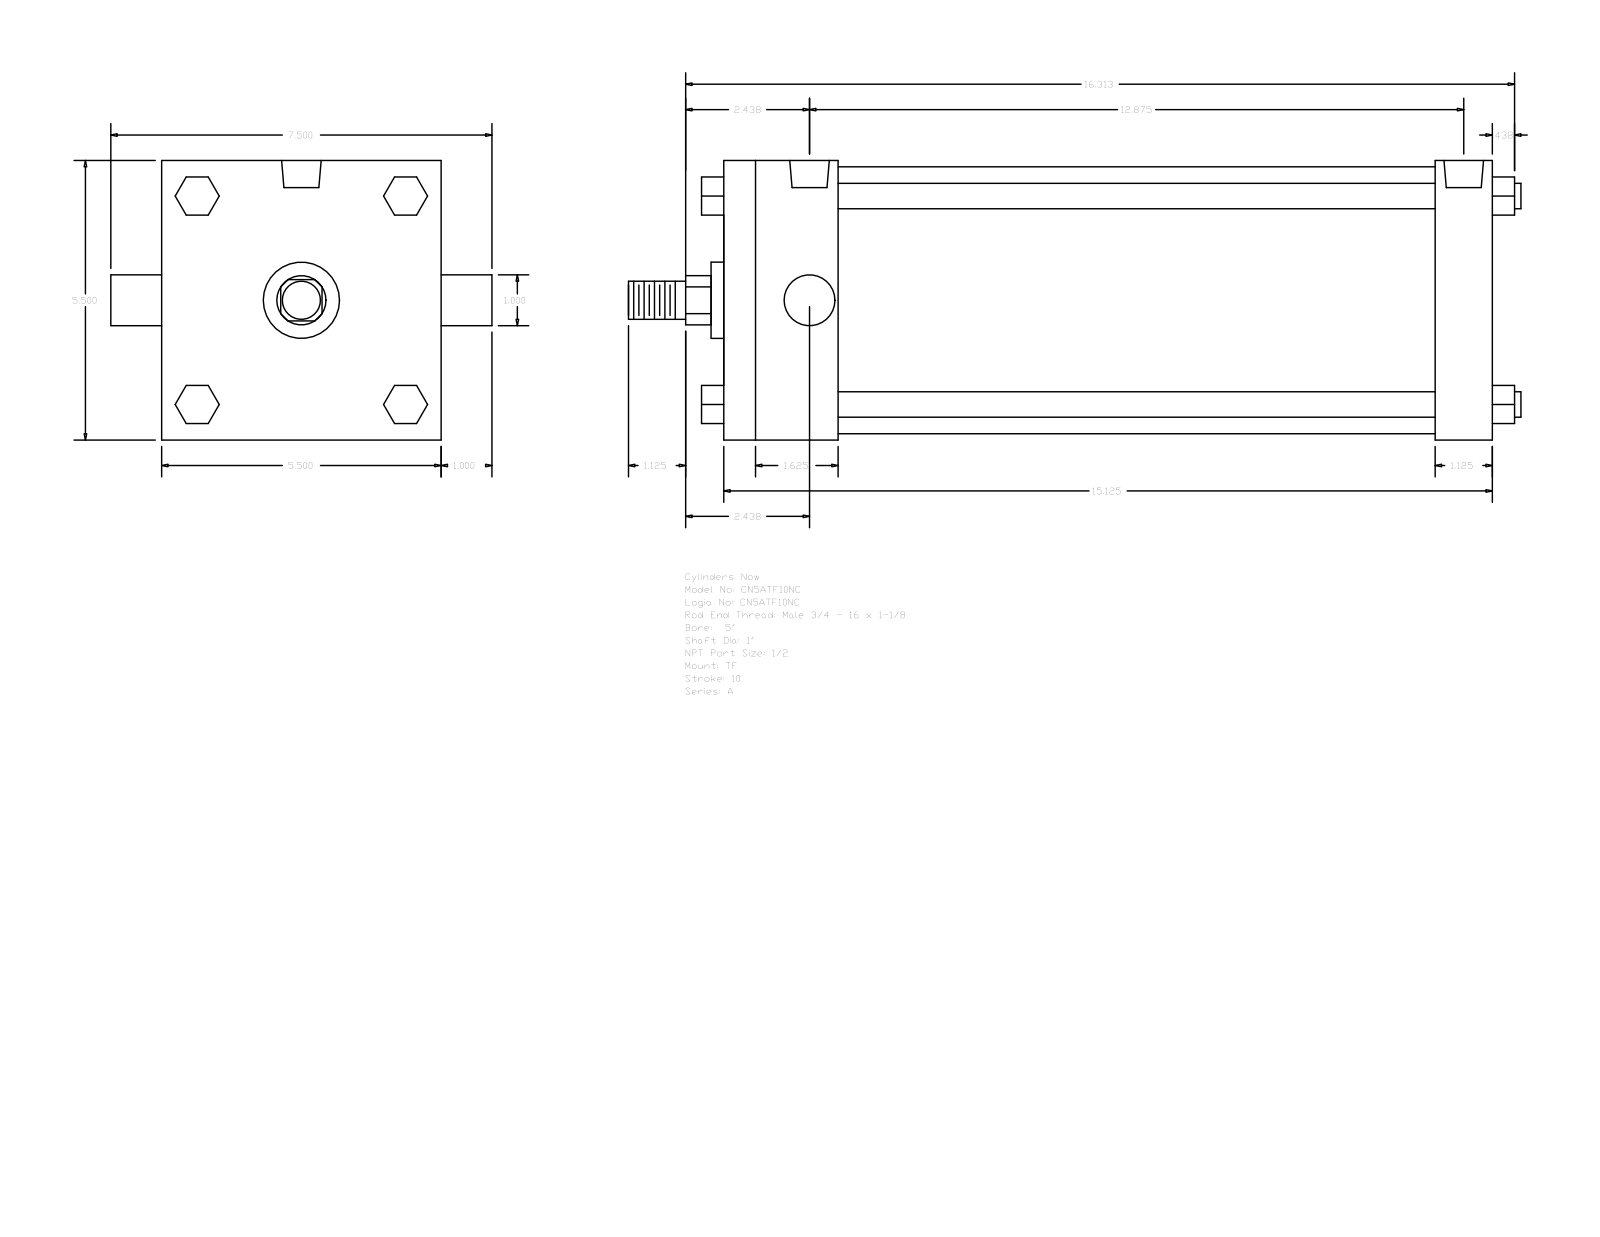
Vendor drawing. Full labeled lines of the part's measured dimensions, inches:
Part name (STEP PRODUCT): A_TF__0500_1
STEP written by: GSSL Pune (CONFIG_CONTROL_DESIGN)
Units: inches
Bodies: 0 solids, 120 faces (92 planar, 28 cylindrical, 0 other)
Overall size (bounding box): 17.563 × 7.5 × 5.5
Round holes (diameter × count): ⌀0.344 ×3, ⌀0.778 ×2
Round bosses / shafts (diameter × count): ⌀0.5 ×4, ⌀1 ×2, ⌀5.25 ×1, ⌀1.5 ×1, ⌀0.75 ×1
Partial cylindrical surfaces — rounded edges, fillets, slot ends (radius × count): R0.484 ×1
Main face-to-face distances: 5.5, 15.125, 14, 1.125, 2.25, 11.75, 12.875, 0.75, 2.05, 3.55
Hole centre spacings: 0.094, 12.781, 12.687, 12.875
